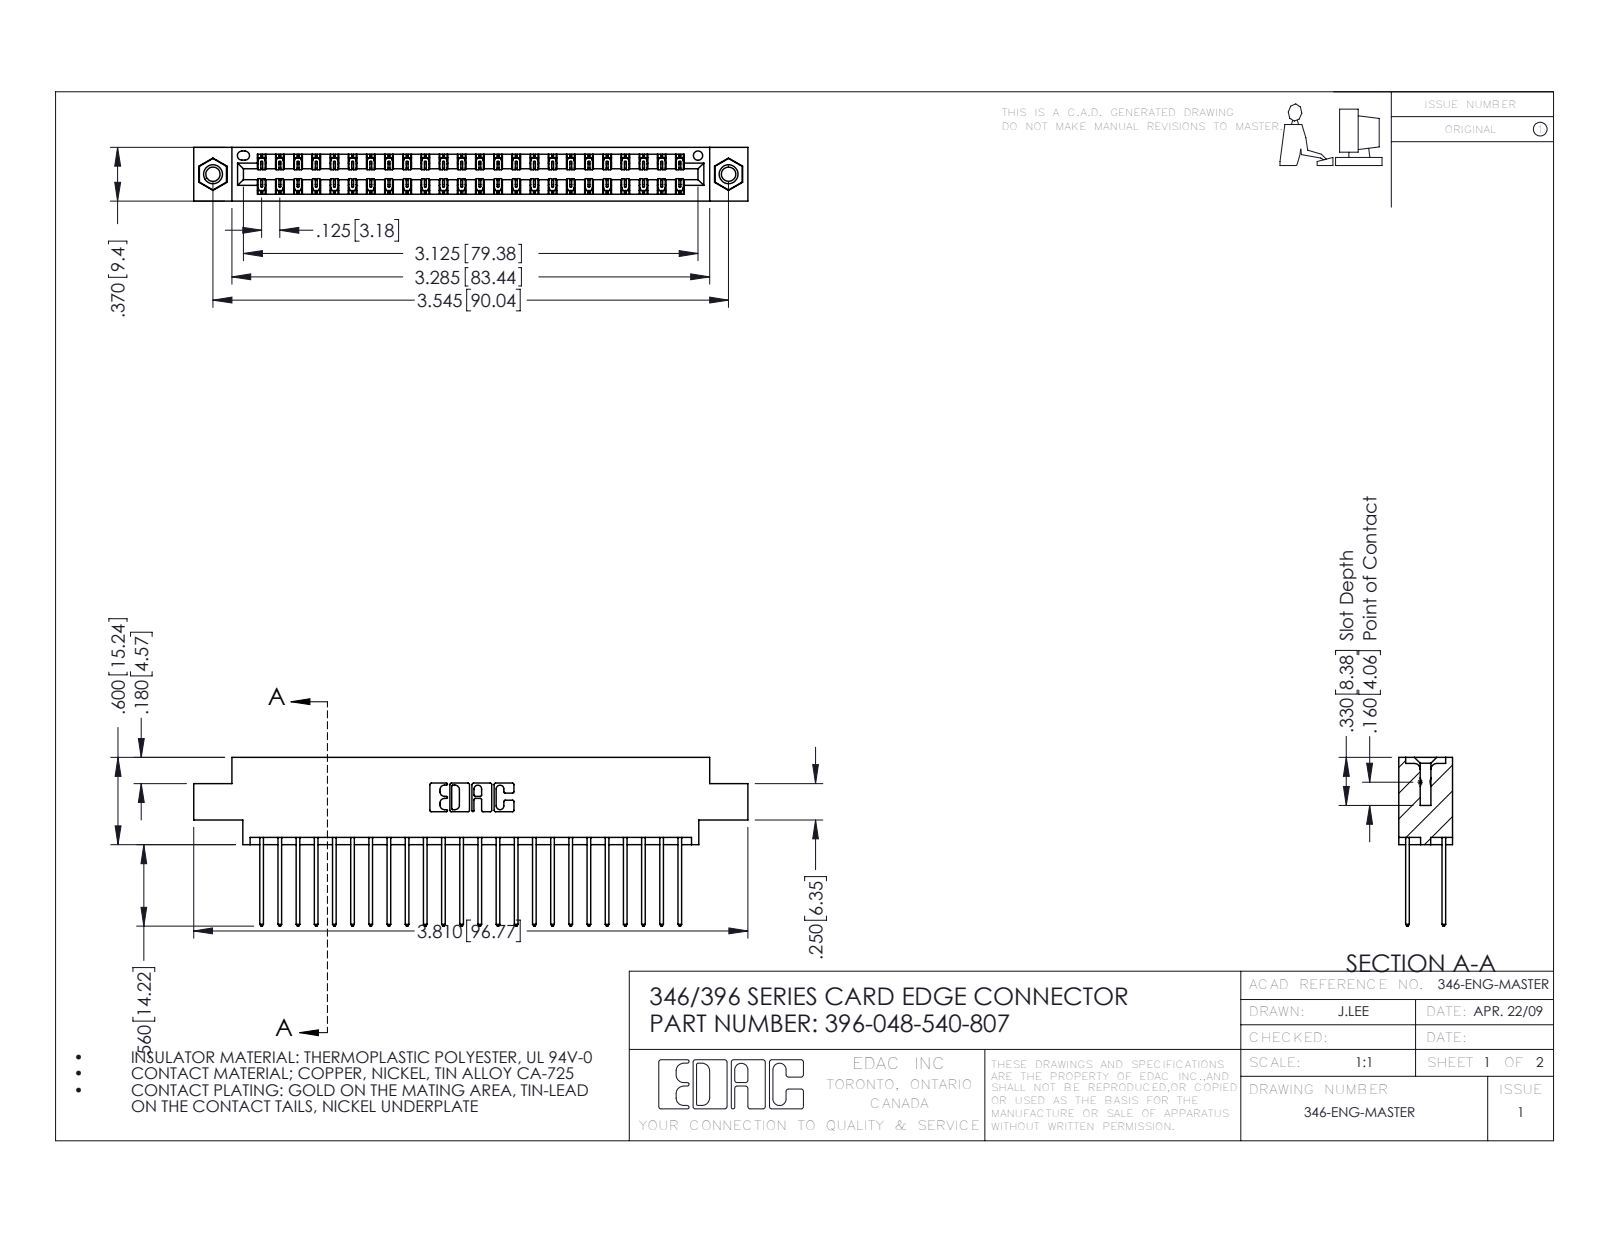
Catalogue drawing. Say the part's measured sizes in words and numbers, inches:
The part is named "346 Part_0.170 Offset - 0.156 Dia-TI; 345-250-001_345-250-005-103; 396-048-540-807; 345-292-001_345-293-140". Its 3-D file was written by "SolidWorks 2016 (CONFIG_CONTROL_DESIGN)". It is 51 solids with 2682 faces: 1792 planar, 874 cylindrical and 16 other. Overall it measures 3.81 by 1.16 by 0.37 inches. Its volume is 0.568 cubic inches and its surface area 21.06 square inches. Round holes: 2 of diameter 0.098, 2 of diameter 0.125, 2 of diameter 0.156, 1 of diameter 0.064. Round bosses or shafts: 2 of diameter 0.155. Partial cylindrical surfaces (rounded edges, fillets, slot ends): 72 of radius 0.006, 48 of radius 0.01, 22 of radius 0.01, 6 of radius 0.007, 6 of radius 0.031, 3 of radius 0.026, 2 of radius 0.014, 2 of radius 0.022. The main face-to-face distances are 0.048, 0.322, 0.25, 0.37, 0.072, 0.298, 0.025, 0.275, 0.222, 0.148. The hole center spacings are 0.246, 3.337, 3.545.
